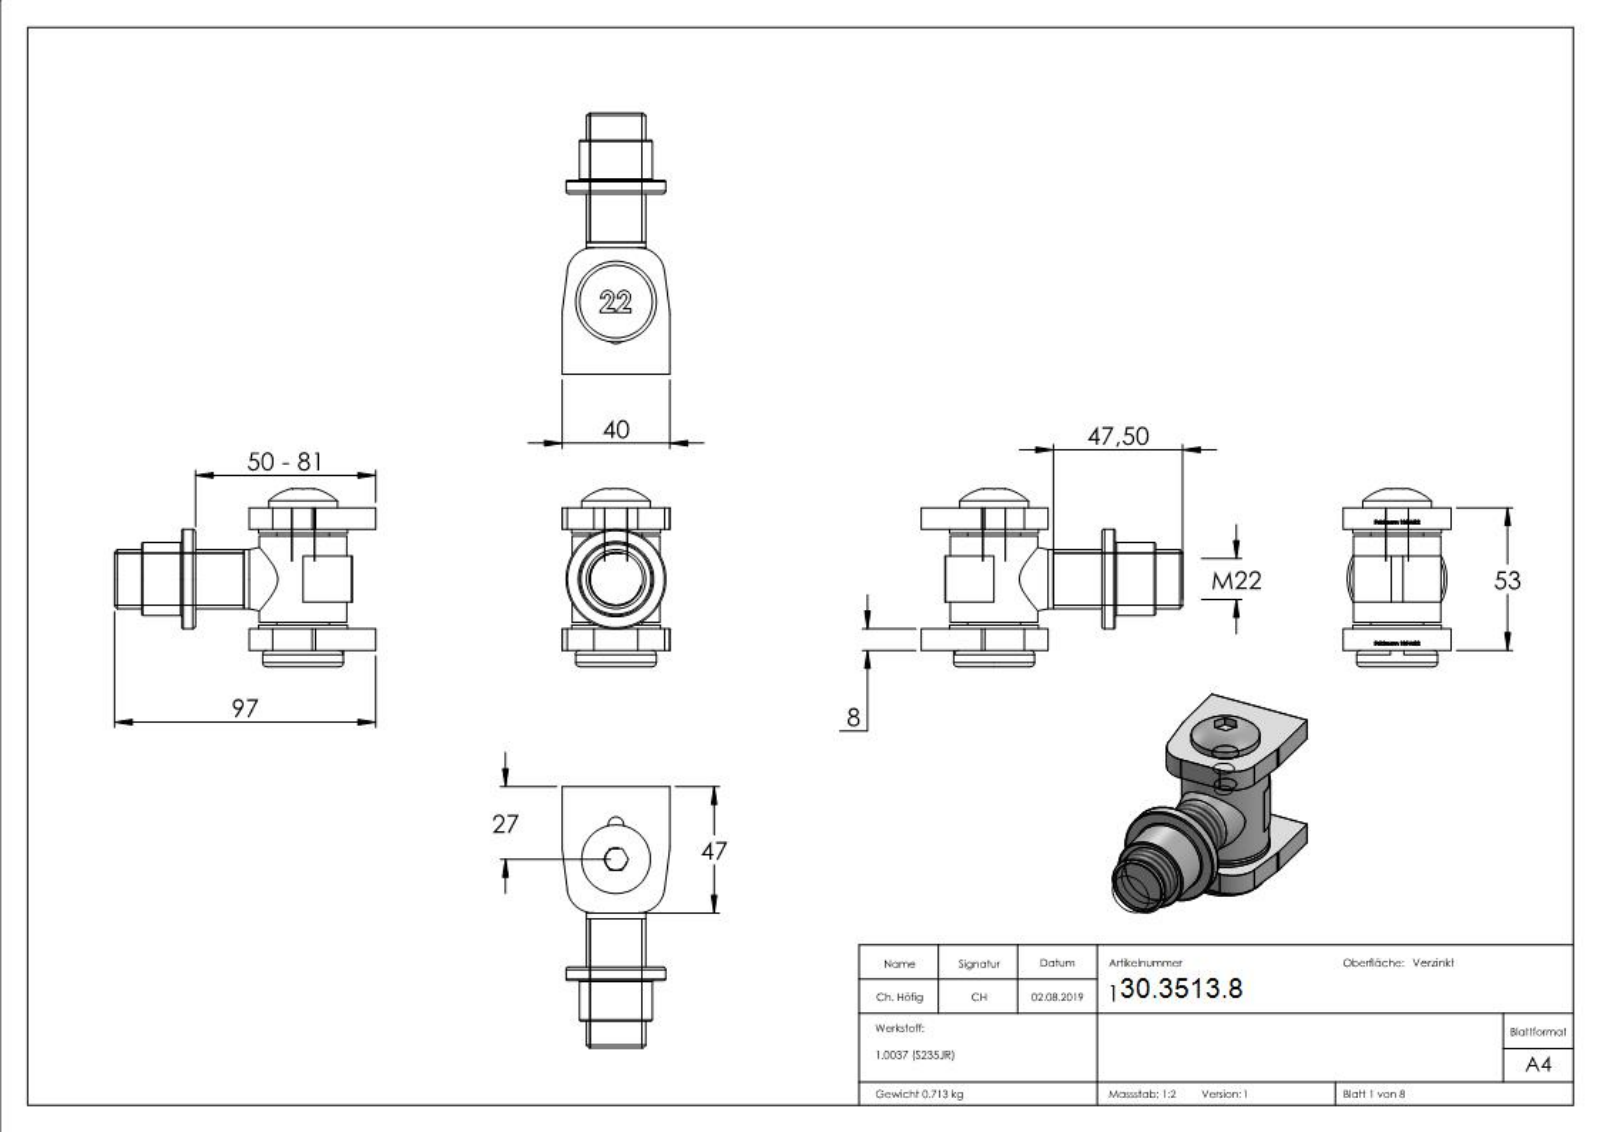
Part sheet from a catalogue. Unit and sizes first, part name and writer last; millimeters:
Units: millimetres
Overall size (bounding box): 97 × 66.07 × 40
Round holes (diameter × count): ⌀8.5 ×1, ⌀12 ×1, ⌀19.5 ×1, ⌀20 ×1, ⌀20.2 ×1, ⌀22 ×1
Round bosses / shafts (diameter × count): ⌀37 ×1, ⌀33 ×1, ⌀32.5 ×1, ⌀30 ×1, ⌀27 ×1, ⌀25.5 ×1, ⌀22 ×1, ⌀19.5 ×1
Partial cylindrical surfaces — rounded edges, fillets, slot ends (radius × count): R10 ×5, R18 ×2, R2.9 ×1
Main face-to-face distances: 8, 45, 37, 53, 10.5, 42.5, 2.5, 34.5, 9.4, 1.4
Volume: 92 573 mm³ · Surface area: 34 370 mm²
Bodies: 8 solids, 552 faces (296 planar, 50 cylindrical, 206 other)
Part name (STEP PRODUCT): 135-MXX Teil6_135-M22 Teil6; 135-MXX Teil1_135-M22 Teil1; 135-MXX Teil3_135-M22 Teil3; 135-MXX Teil2_135-M22 Teil2 (+3 more)
STEP written by: SolidWorks 2015 (CONFIG_CONTROL_DESIGN)
